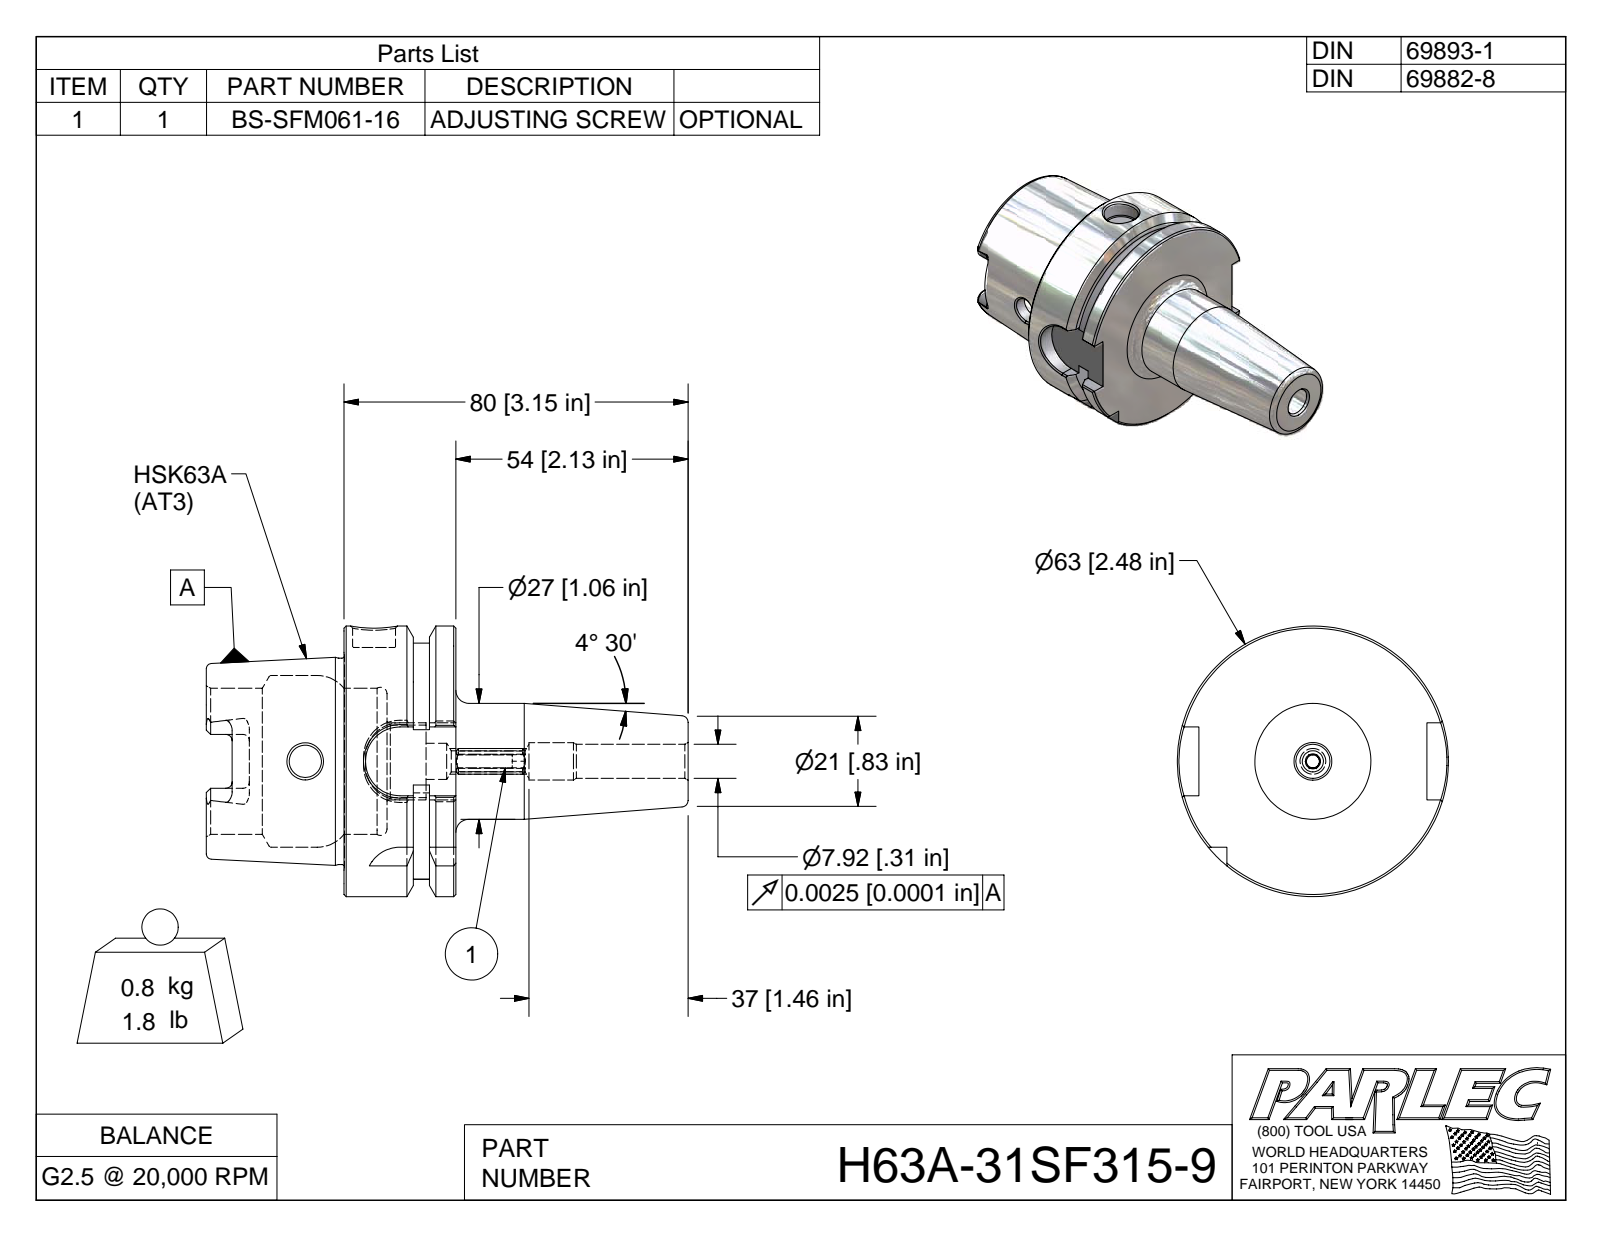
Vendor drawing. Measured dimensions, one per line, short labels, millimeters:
name: H63A-31SF315-9; H63A-31SF315-9-1; BS-SFM061-16
written by: Autodesk Inventor 2009 (AUTOMOTIVE_DESIGN)
unit: mm
bodies: 2 solids, 162 faces (58 planar, 35 cylindrical, 69 other)
size: 112 × 63 × 63
volume: 106 400 mm³; area: 27 880 mm²
holes: 1× ⌀7.5, 1× ⌀7.9, 1× ⌀8.7, 1× ⌀10, 1× ⌀16.9, 1× ⌀34, 1× ⌀40
bosses: 1× ⌀63, 1× ⌀48, 1× ⌀27
rounds: 6× R1.5, 4× R2.9, 4× R8, 1× R3, 1× R27.5
face distances: 26, 6.1, 9.9, 10, 16, 32, 42, 58, 48.1, 16.1
